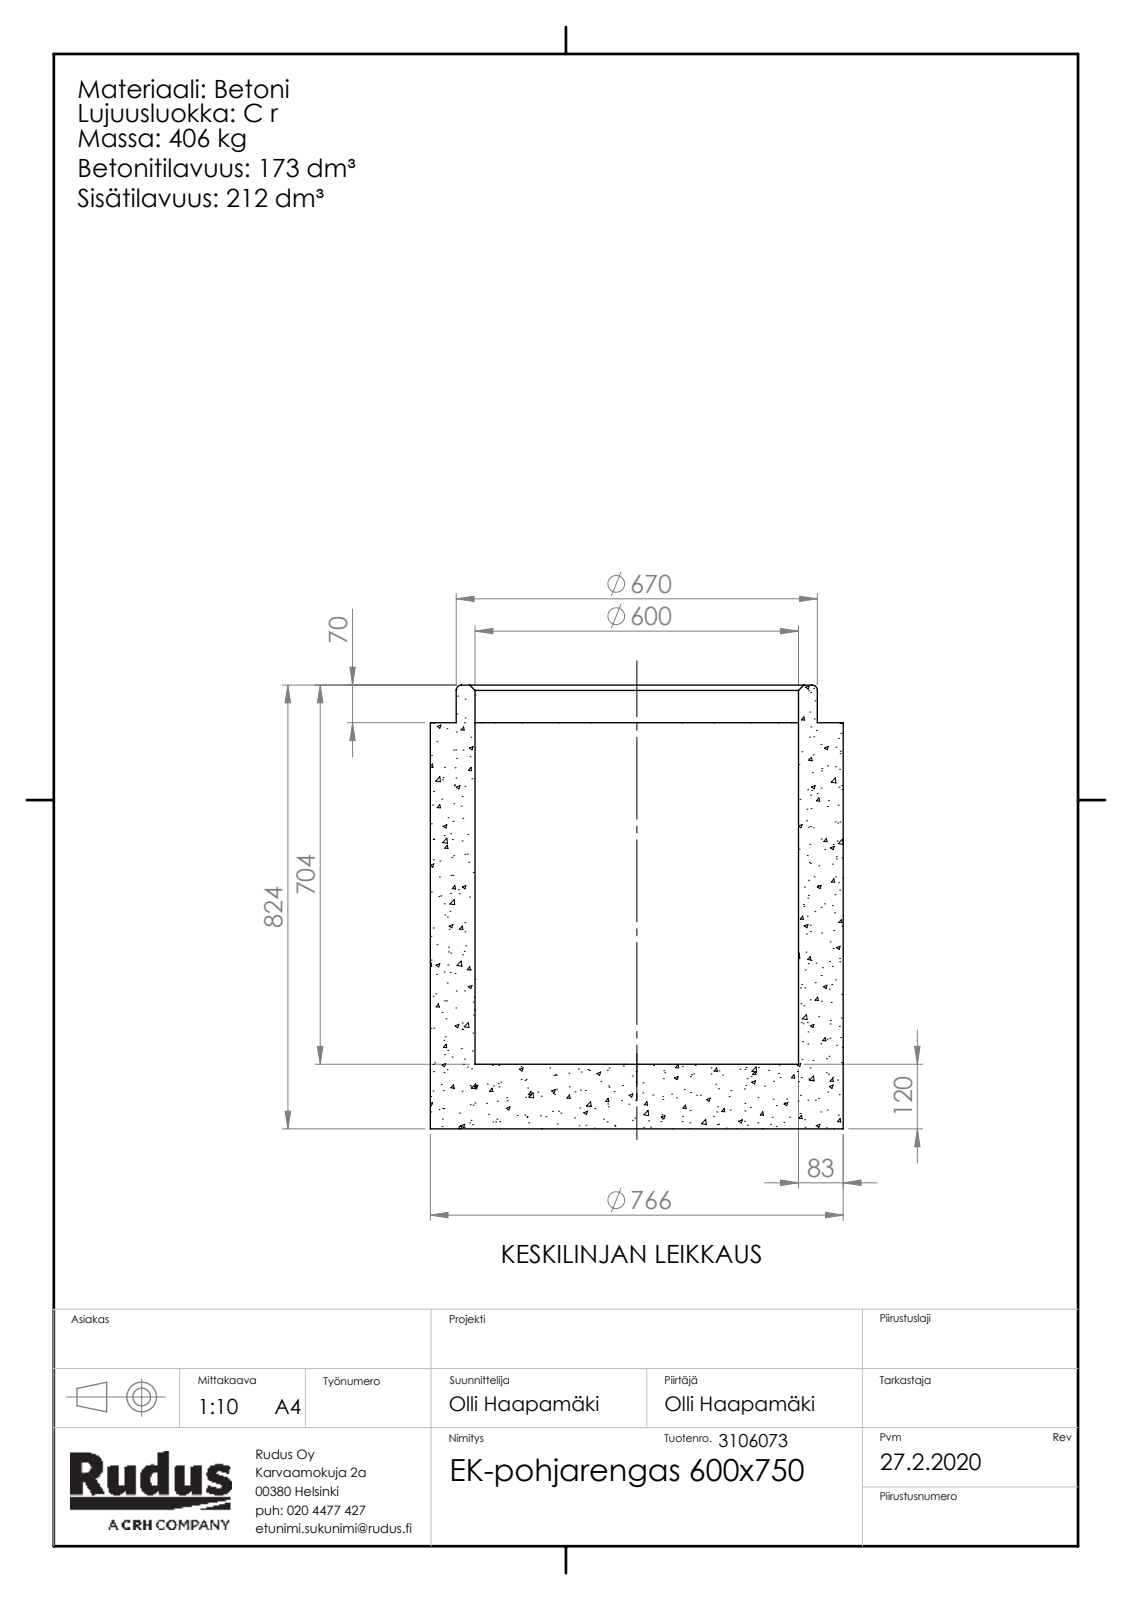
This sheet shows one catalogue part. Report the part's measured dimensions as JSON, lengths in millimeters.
{"part_name": "Rudus 3106073 EK-pohjarengas 600x750; EK-osa-kaivorunko_EK-pohjarengas", "step_written_by": "SolidWorks 2019 (CONFIG_CONTROL_DESIGN)", "units": "millimeters", "bodies": {"solids": 1, "faces": 95, "planar": 4, "cylindrical": 6, "other": 85}, "overall_size": [824, 766, 766], "volume_mm3": 173000000, "surface_area_mm2": 4195000, "round_holes": [[600, 1]], "round_bosses_or_shafts": [[766, 1], [670, 1]], "face_to_face_distances": [120, 754, 634, 824, 704, 70]}
